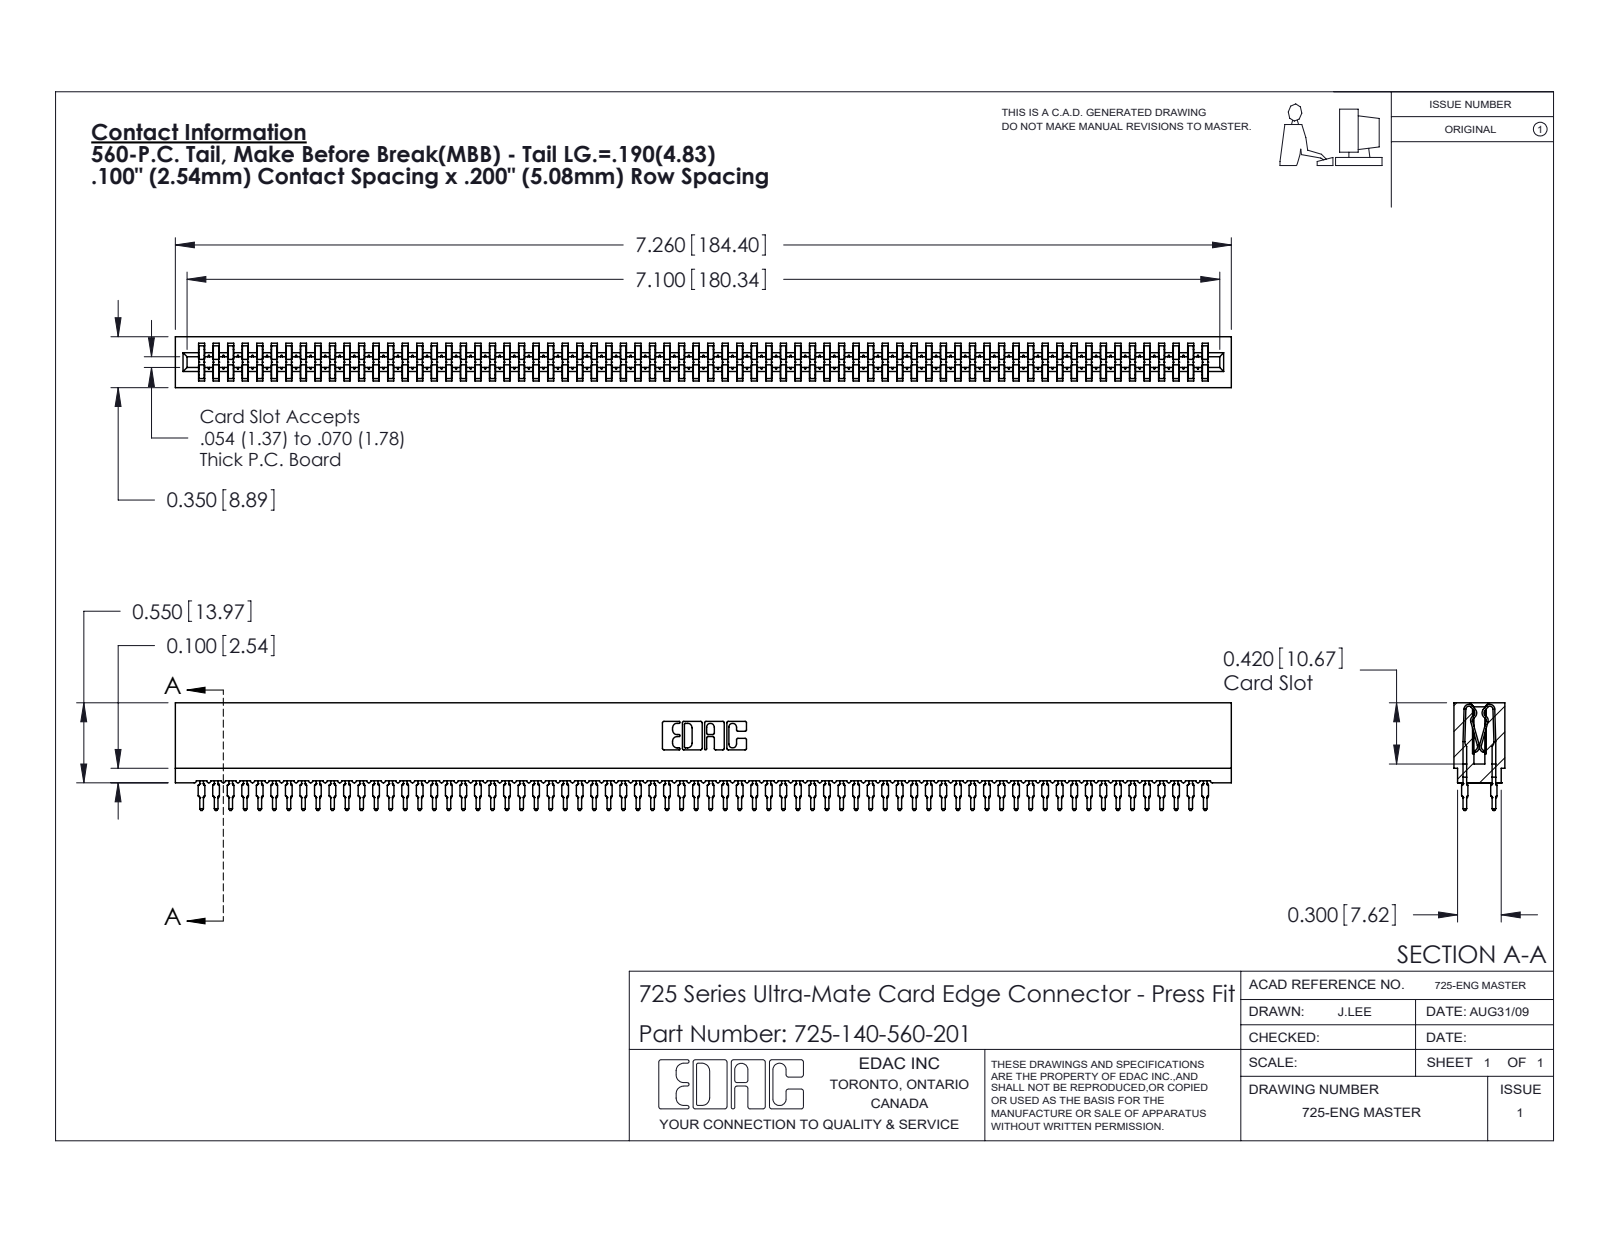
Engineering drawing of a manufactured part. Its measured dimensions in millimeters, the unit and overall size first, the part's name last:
Units: millimetres
Overall size (bounding box): 184.4 × 18.8 × 8.9
Partial cylindrical surfaces — rounded edges, fillets, slot ends (radius × count): R0.5 ×280, R0.4 ×140, R0.3 ×22, R0.1 ×8, R0.3 ×8, R0.2 ×6, R0.8 ×6, R0.7 ×3
Main face-to-face distances: 5.1, 1.6, 7.3, 8.9, 5.4, 3.5, 1.9, 3.8, 1.1, 7.7
Volume: 15 000 mm³ · Surface area: 34 490 mm²
Bodies: 141 solids, 13885 faces (7195 planar, 3050 cylindrical, 3640 other)
Part name (STEP PRODUCT): 745-292-001_560; 725-140-560-201; 725 Part_Insulator Option - 01
STEP written by: SolidWorks 2020 (CONFIG_CONTROL_DESIGN)
